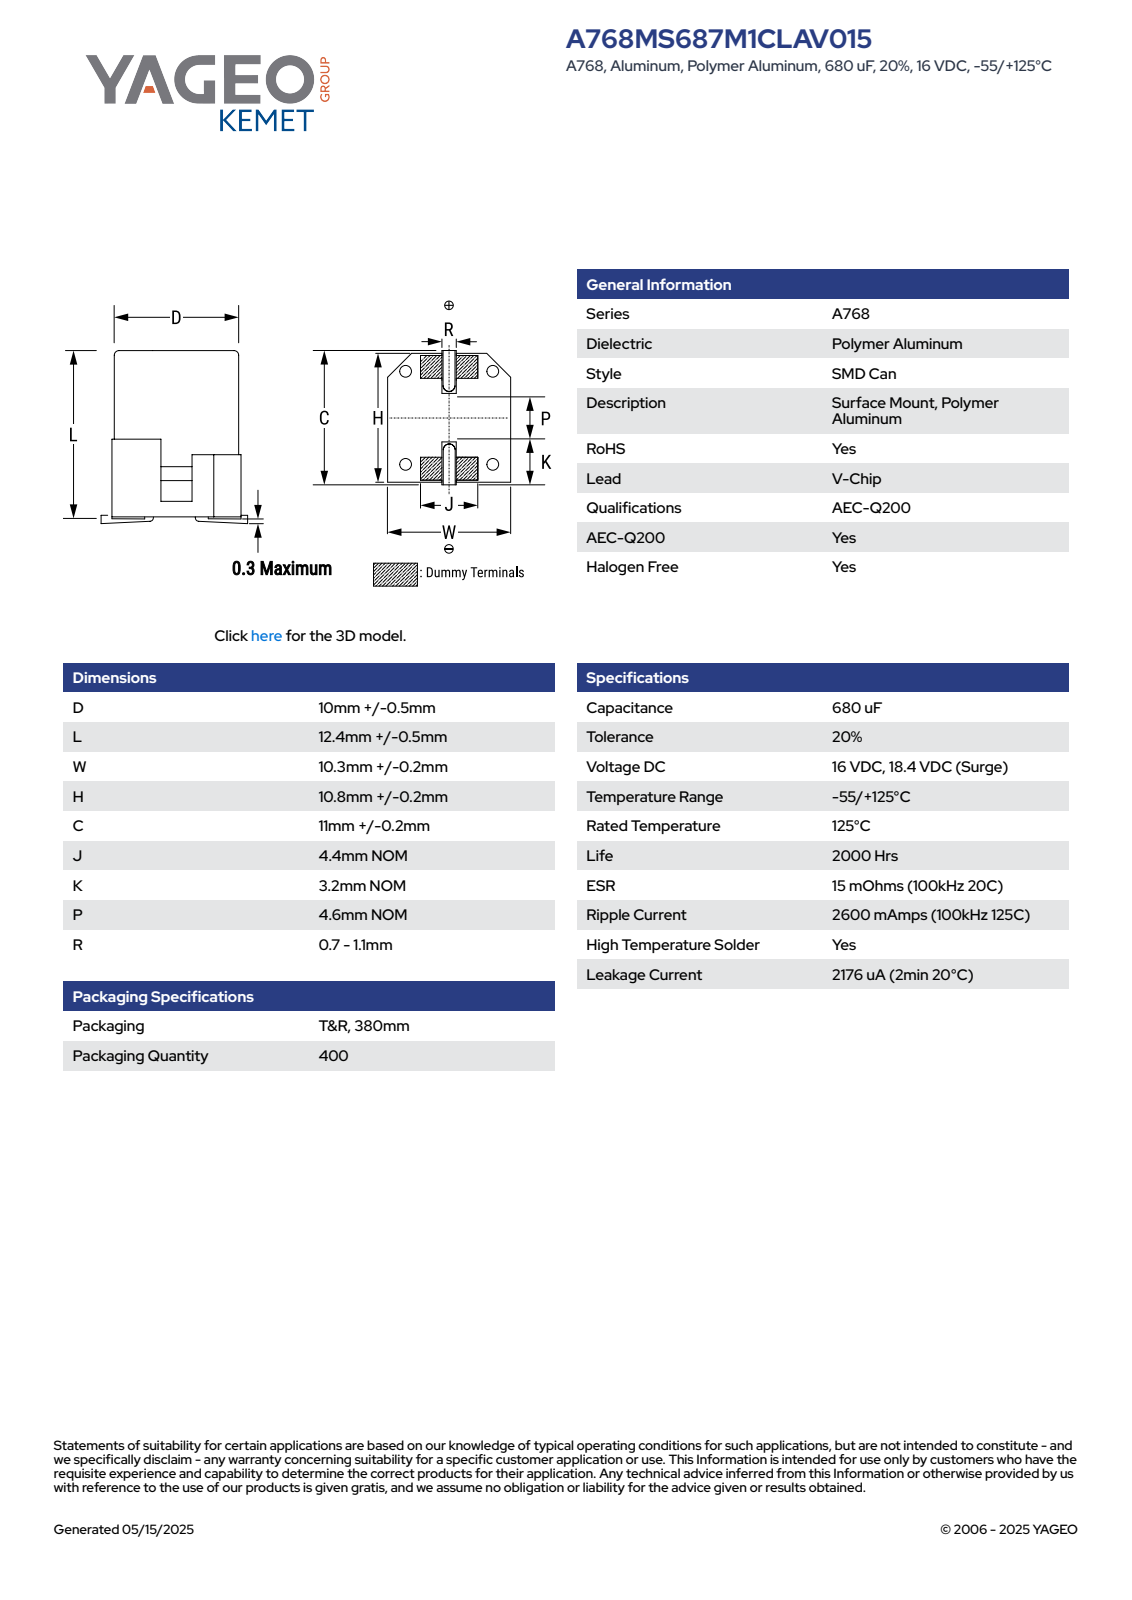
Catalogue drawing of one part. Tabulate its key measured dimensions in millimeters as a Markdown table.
| quantity | value |
| --- | --- |
| part name | CAC_KAV_10X12.2_D10.5L12.7W1.1F0.2A10.5B10.5C11.2P3.2 |
| STEP written by | SolidWorks 2014 (AUTOMOTIVE_DESIGN) |
| units | millimeters |
| bodies | 5 solids, 76 faces (59 planar, 11 cylindrical, 6 other) |
| overall size | 12.71 × 11.2 × 10.5 |
| volume | 1 060 mm³ |
| surface area | 941 mm² |
| round bosses / shafts (diameter × count) | 10.04 × 1 |
| partial cylindrical surfaces (radius × count) | 0.2 × 2, 4.17 × 1, 5.25 × 1 |
| main face-to-face distances | 1.02, 10.5, 12.5, 11.48, 12.51, 11.49, 5.08, 4.06, 7.42, 7.43 |
